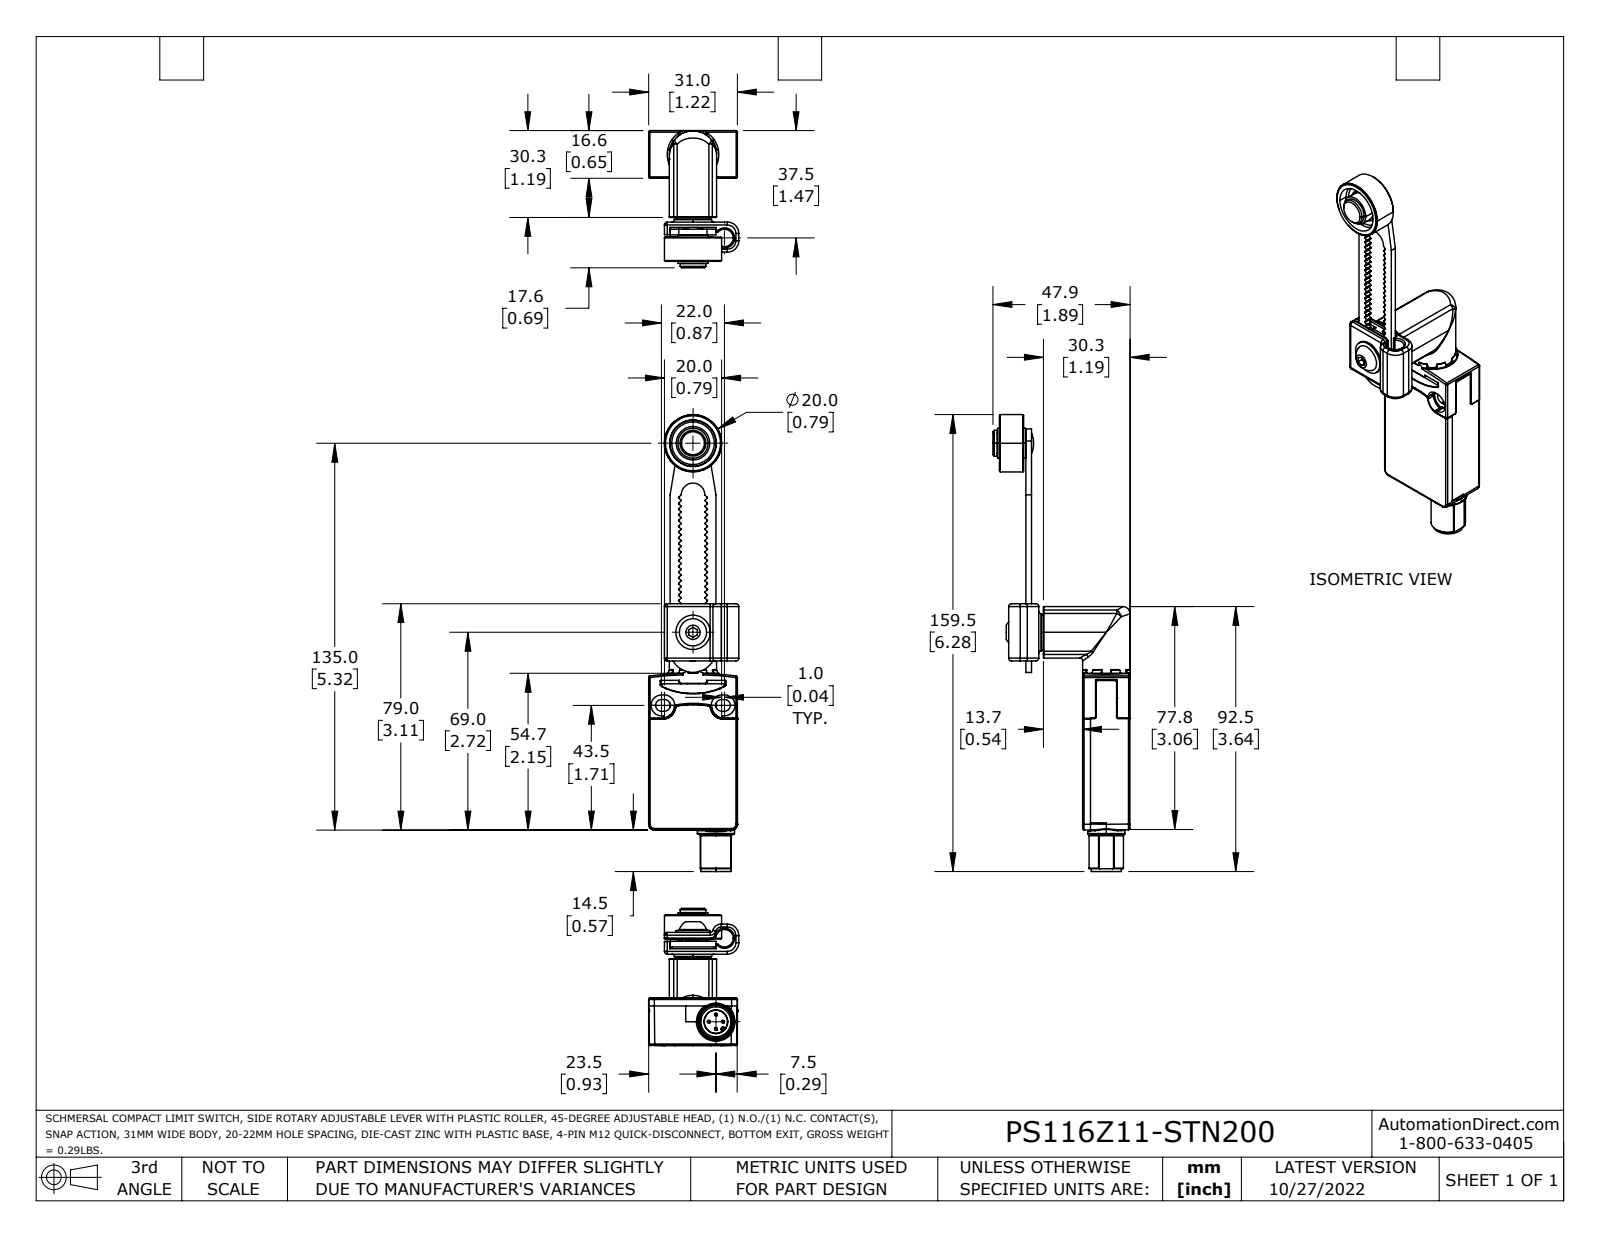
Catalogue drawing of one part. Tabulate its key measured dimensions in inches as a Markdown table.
| quantity | value |
| --- | --- |
| part name | PS116Z11-STN200_Default |
| STEP written by | SolidWorks 2021 (CONFIG_CONTROL_DESIGN) |
| units | inches |
| bodies | 1 solid, 1429 faces (442 planar, 688 cylindrical, 299 other) |
| overall size | 6.281 × 1.886 × 1.24 |
| volume | 2.582 in³ |
| surface area | 32.08 in² |
| round holes (diameter × count) | 0.079 × 1, 0.24 × 1, 0.315 × 1, 0.327 × 1, 0.48 × 1, 0.571 × 1, 0.583 × 1 |
| round bosses / shafts (diameter × count) | 0.039 × 4, 0.512 × 2, 0.413 × 2, 0.787 × 1, 0.65 × 1, 0.567 × 1, 0.524 × 1, 0.475 × 1 |
| partial cylindrical surfaces (radius × count) | 0.008 × 229, 0.004 × 67, 0.02 × 41, 0.039 × 27, 0.079 × 12, 0.014 × 10, 0.118 × 5, 0.081 × 4 |
| main face-to-face distances | 0.65, 0.781, 0.079, 1.431, 1.352, 0.703, 0.652, 0.098, 0.177, 0.201 |
| hole center spacings | 0.315, 1.154, 1.227, 2.598 |
